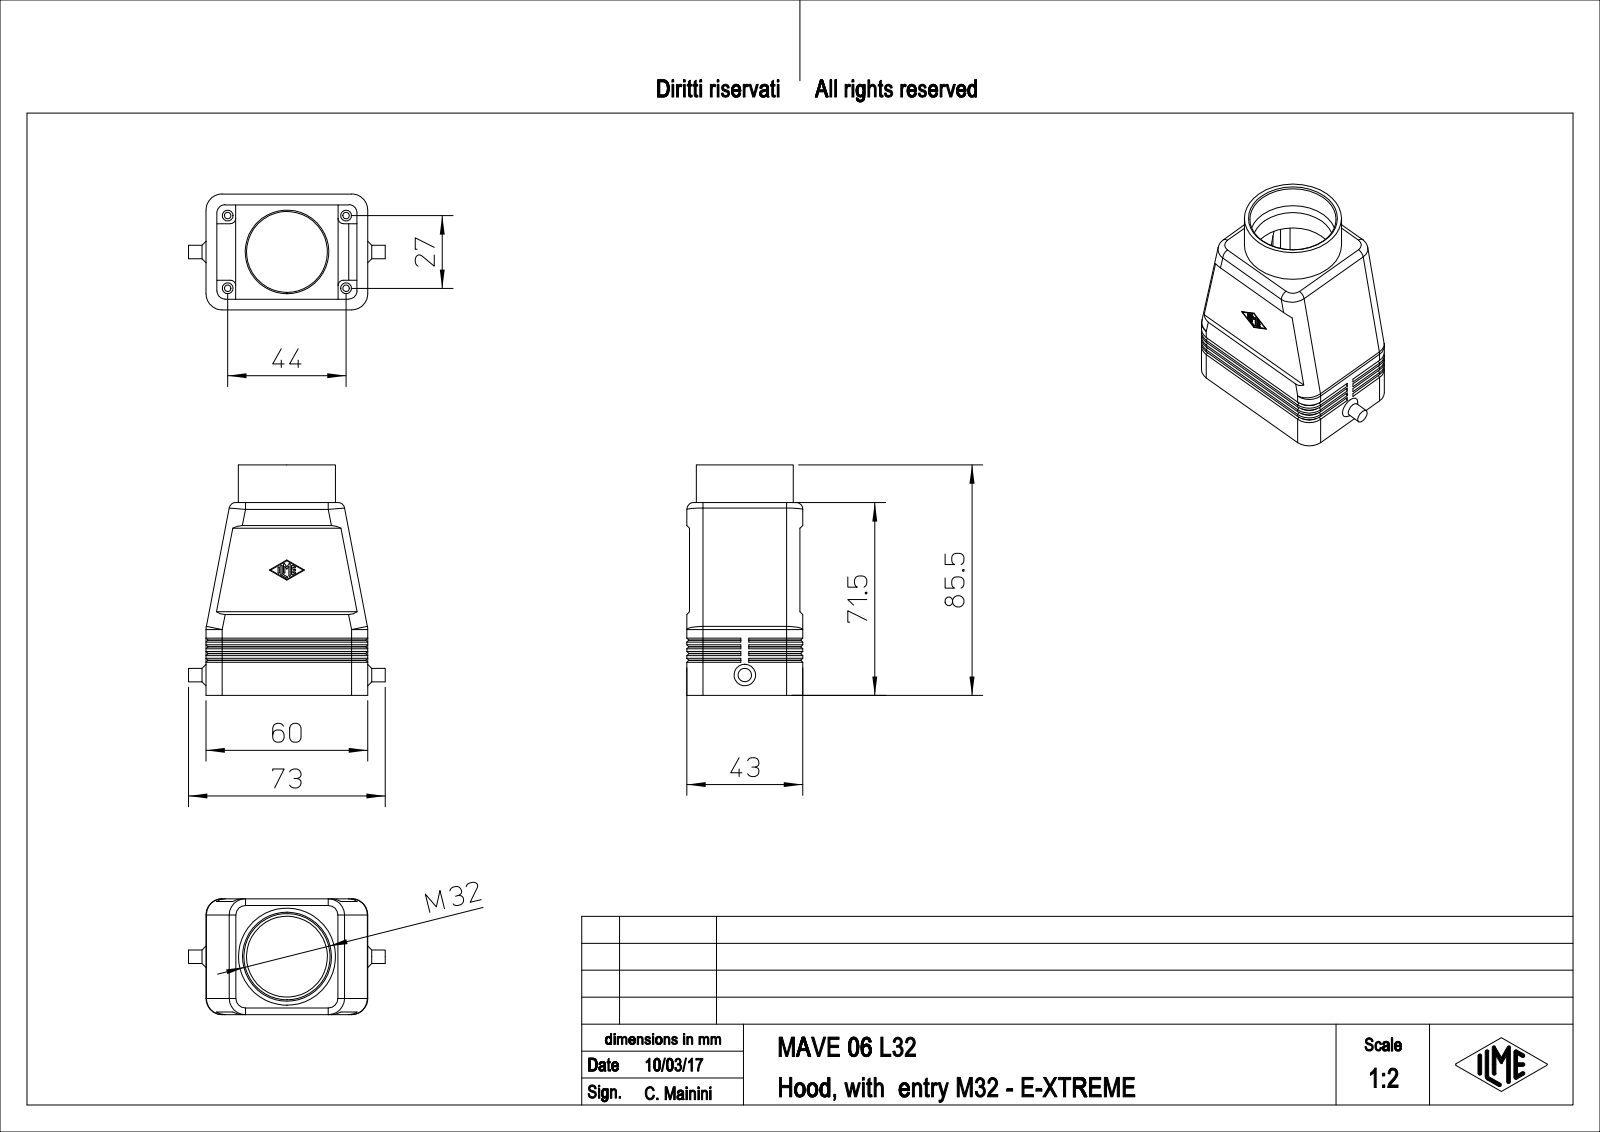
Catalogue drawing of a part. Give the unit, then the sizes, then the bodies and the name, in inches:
Units: inches
Overall size (bounding box): 3.366 × 2.874 × 1.693
Round holes (diameter × count): ⌀0.097 ×4, ⌀0.157 ×4, ⌀1.181 ×1, ⌀1.26 ×1
Round bosses / shafts (diameter × count): ⌀1.417 ×1, ⌀1.22 ×1, ⌀0.197 ×1
Partial cylindrical surfaces — rounded edges, fillets, slot ends (radius × count): R0.01 ×14, R0.236 ×10, R0.079 ×4, R0.098 ×4, R0.118 ×4, R0.209 ×4
Main face-to-face distances: 0.157, 1.496, 0.118, 0.039, 1.535, 1.654, 1.378, 0.276, 0.433, 1.614
Hole centre spacings: 1.016, 1.063, 1.732, 2.032
Volume: 3.442 in³ · Surface area: 48.12 in²
Bodies: 1 solid, 329 faces (177 planar, 96 cylindrical, 56 other)
Part name (STEP PRODUCT): MAVE_06_L32
STEP written by: PTC Creo Elements/Direct Modeling 19.0E 27-Jun-2016 (C) Parametric Technology GmbH (AUTOMOTIVE_DESIGN)
